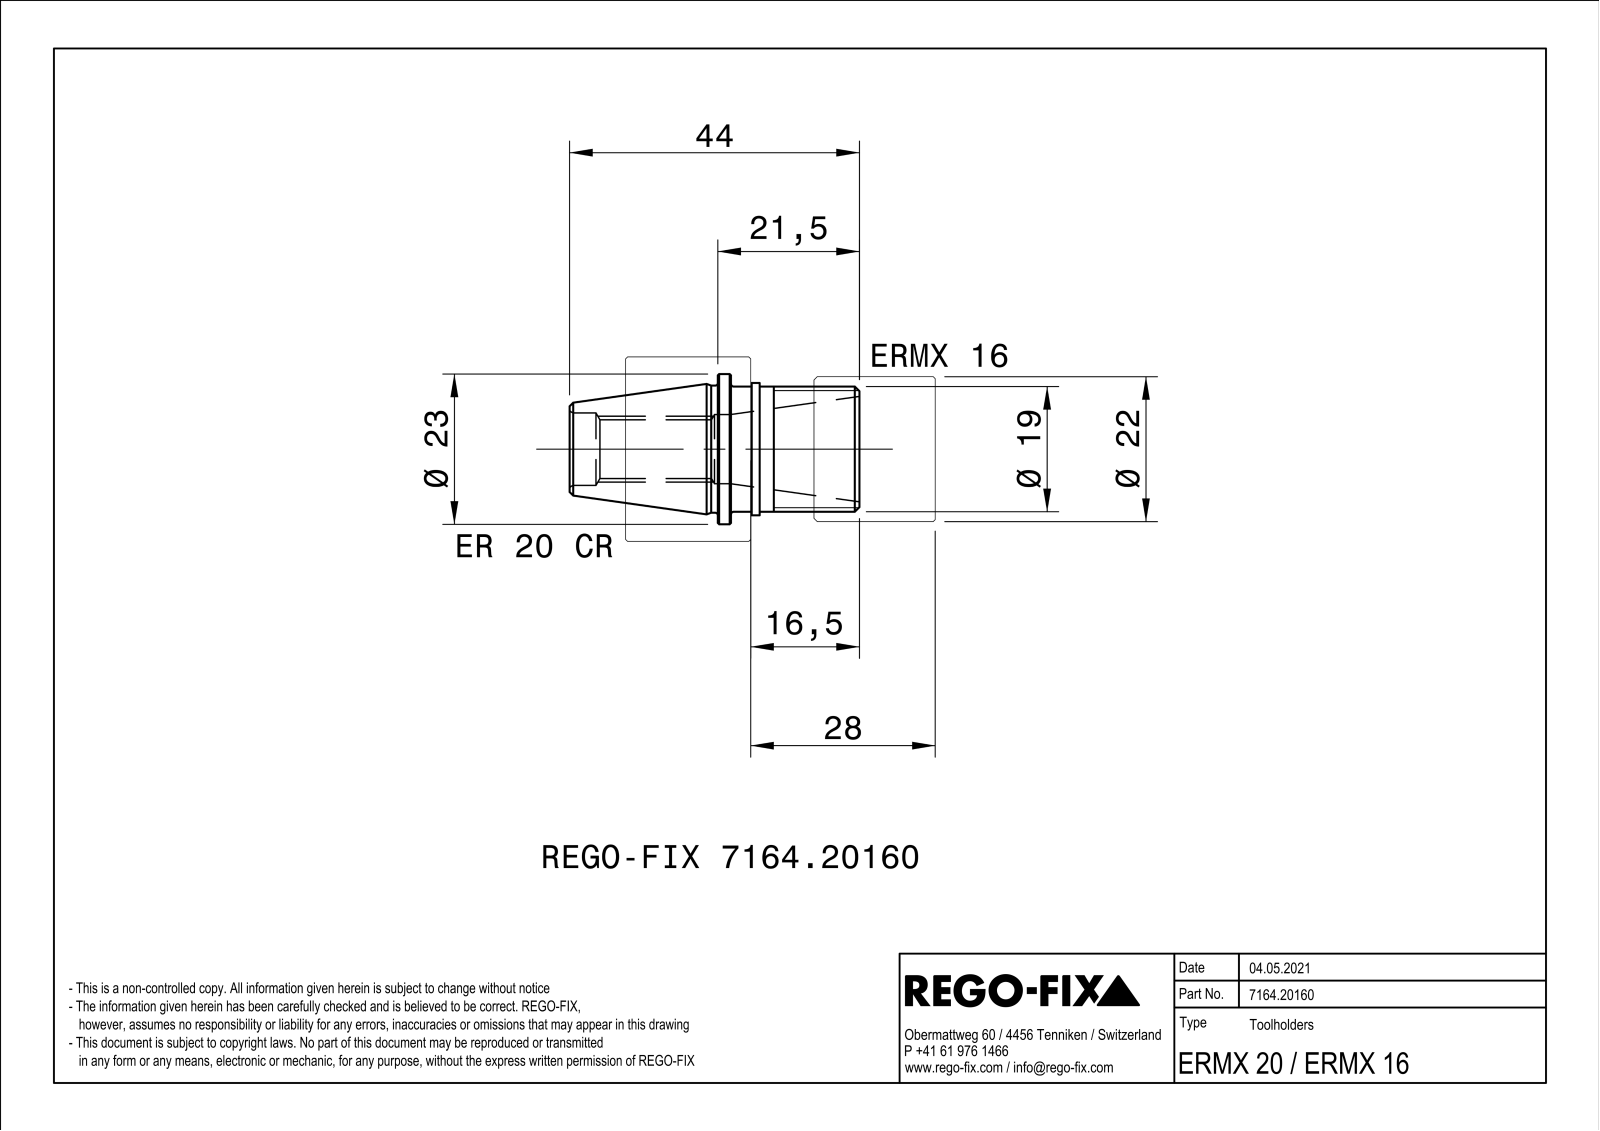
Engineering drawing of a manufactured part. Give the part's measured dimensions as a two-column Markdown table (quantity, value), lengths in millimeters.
| quantity | value |
| --- | --- |
| part name | NOCUT |
| STEP written by | SIEMENS PLM Software Solid Edge ST10 (AUTOMOTIVE_DESIGN) |
| units | millimeters |
| bodies | 1 solid, 78 faces (33 planar, 17 cylindrical, 28 other) |
| overall size | 44 × 28 × 28 |
| volume | 10 295 mm³ |
| surface area | 7 258 mm² |
| round holes (diameter × count) | 8.92 × 1, 10.5 × 1, 11 × 1, 19.4 × 1, 22.92 × 1, 24.3 × 1 |
| round bosses / shafts (diameter × count) | 28 × 1, 23.2 × 1, 22.8 × 1, 19.3 × 1, 19 × 1, 17.9 × 1, 8 × 1 |
| partial cylindrical surfaces (radius × count) | 6 × 2 |
| main face-to-face distances | 1.2, 1.35, 5, 13.85, 12.65, 12.5, 9.5, 6.35, 5.15, 7.5 |
